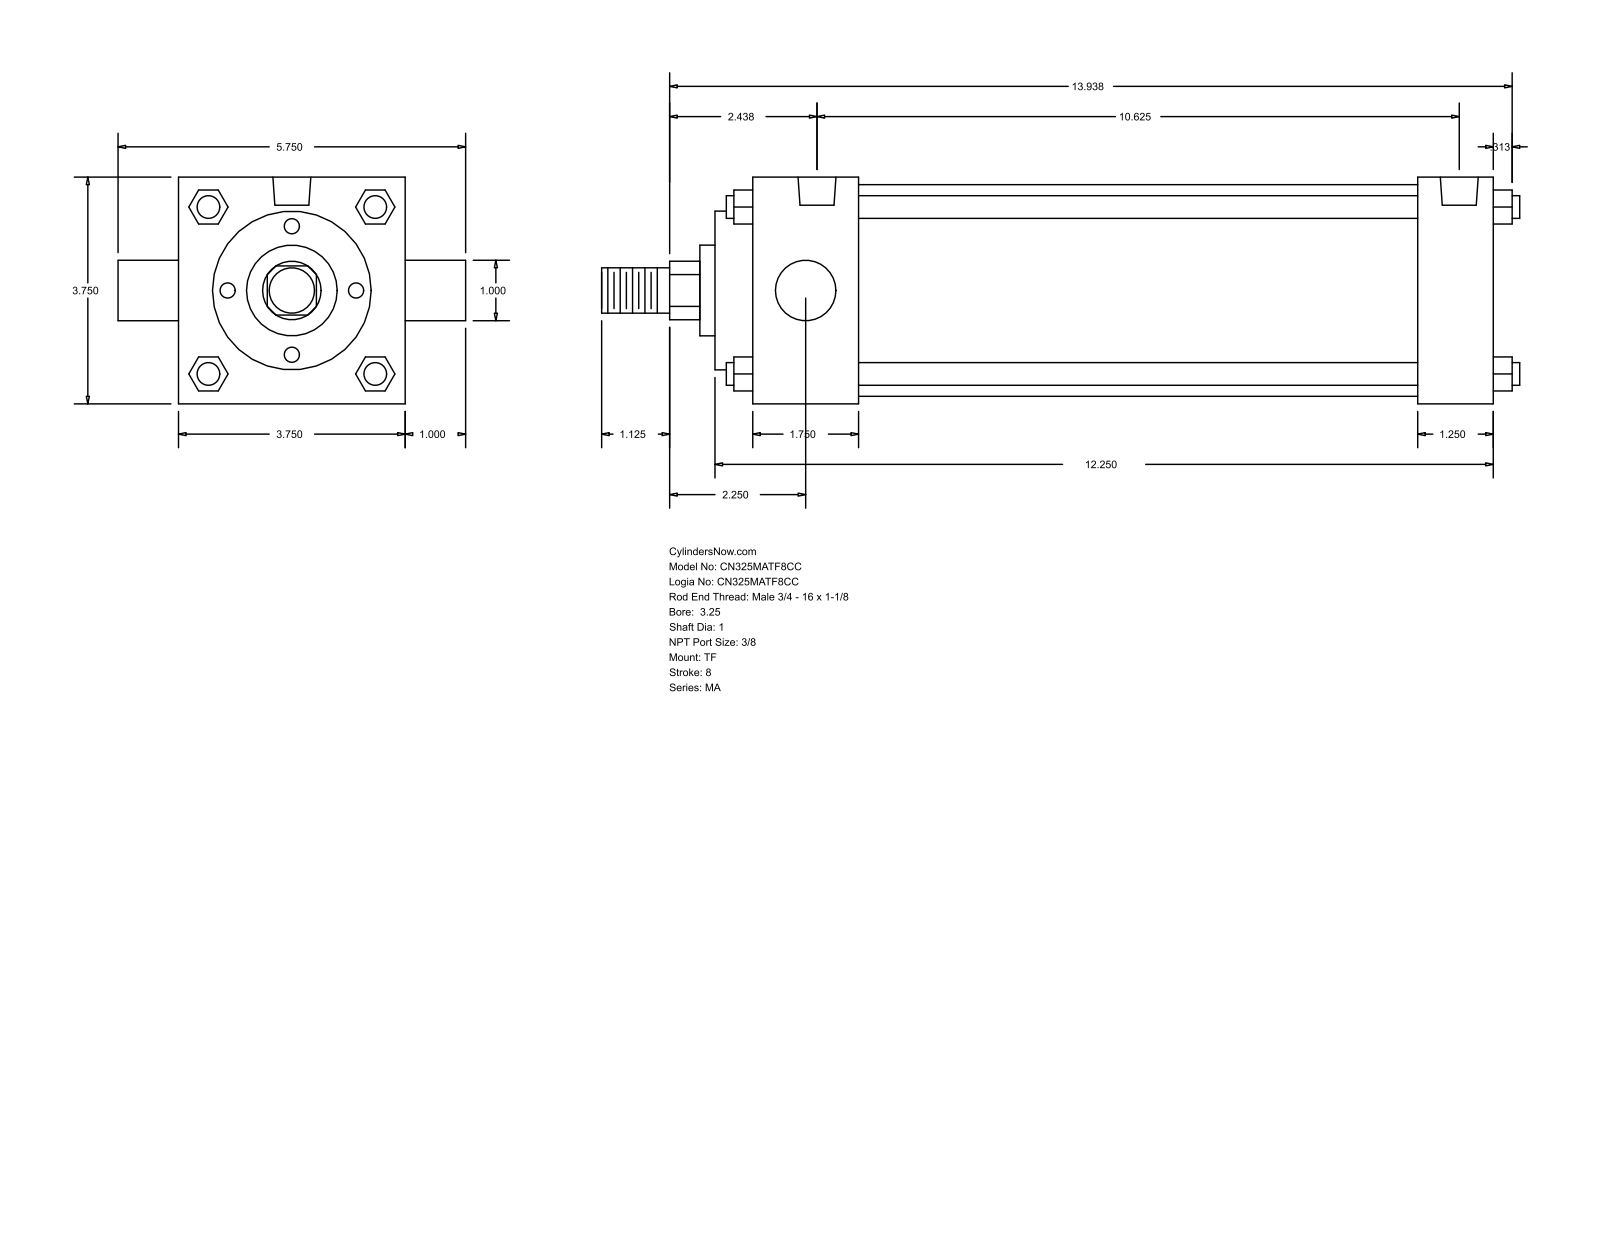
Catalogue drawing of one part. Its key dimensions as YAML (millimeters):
part_name: "MA_TF__0325_1"
step_written_by: "GSSL Pune (CONFIG_CONTROL_DESIGN)"
units: millimeters
bodies: {solids: 0, faces: 122, planar: 93, cylindrical: 29, other: 0}
overall_size: [385.76, 146.05, 95.25]
round_holes:
  - {diameter: 11.11, count: 3}
  - {diameter: 15.93, count: 2}
round_bosses_or_shafts:
  - {diameter: 9.53, count: 4}
  - {diameter: 25.4, count: 2}
  - {diameter: 88.9, count: 1}
  - {diameter: 66.67, count: 1}
  - {diameter: 38.1, count: 1}
  - {diameter: 19.05, count: 1}
partial_cylinders:
  - {radius: 12.29, count: 1}
face_to_face_distances: [95.24, 311.15, 327.02, 44.46, 279.4, 234.94, 266.69, 31.75, 15.87, 60.33]
hole_center_spacings: [4.76, 4.77, 260.35, 265.11, 265.12, 269.88]
